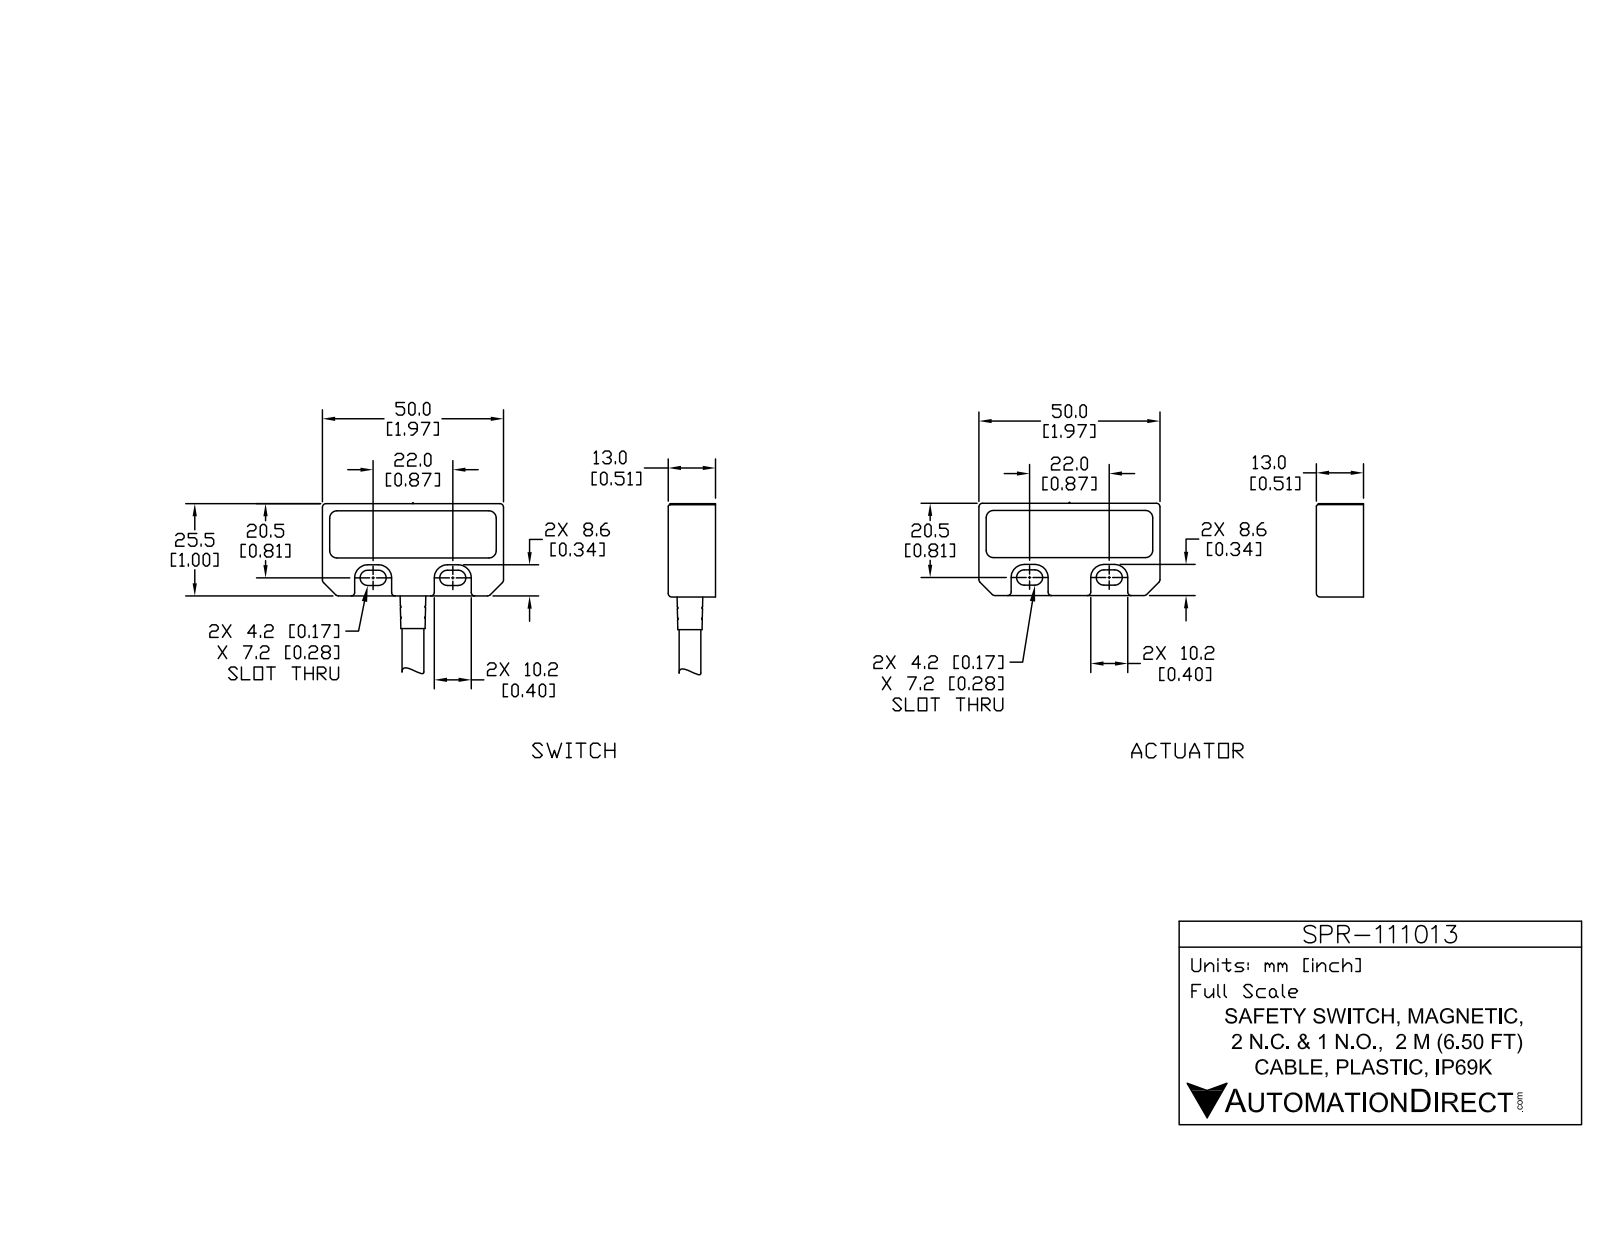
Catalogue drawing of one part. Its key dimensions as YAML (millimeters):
part_name: "SPR-111013_1; SPR-111013; SPR-111013_2"
step_written_by: "SolidWorks 2017 (AUTOMOTIVE_DESIGN)"
units: millimeters
bodies: {solids: 4, faces: 191, planar: 61, cylindrical: 80, other: 50}
overall_size: [149.5, 50, 13.3]
volume: 33810
surface_area: 11750
round_bosses_or_shafts:
  - {diameter: 6, count: 1}
partial_cylinders:
  - {radius: 1, count: 36}
  - {radius: 2, count: 8}
  - {radius: 2.1, count: 8}
  - {radius: 3.6, count: 8}
  - {radius: 0.5, count: 2}
face_to_face_distances: [13, 25.5, 26.5, 13.3, 1, 50, 52, 4.2, 4.5, 8.8]
